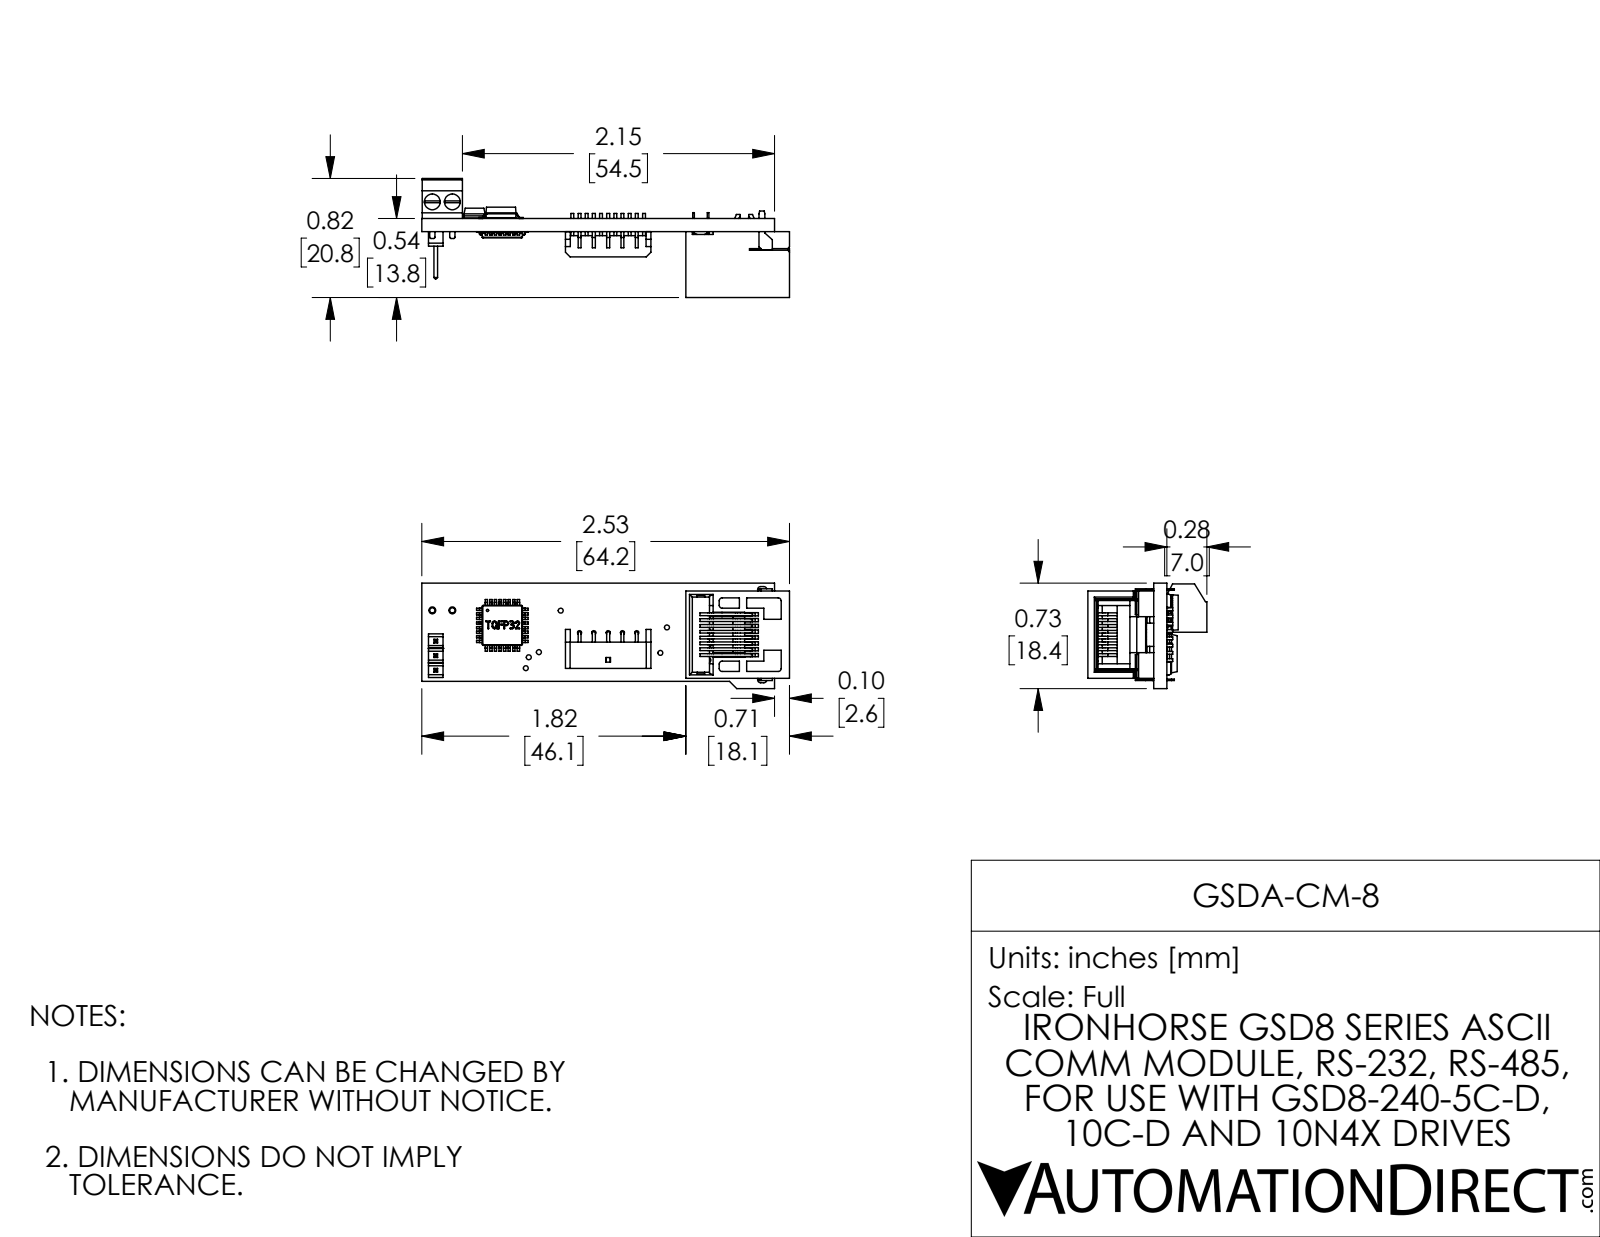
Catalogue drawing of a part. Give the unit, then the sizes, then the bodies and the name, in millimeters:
Units: millimetres
Overall size (bounding box): 64.2 × 20.8 × 18.4
Round holes (diameter × count): ⌀0.9 ×14, ⌀0.7 ×11, ⌀1 ×3, ⌀1.2 ×2, ⌀2 ×2, ⌀2.7 ×2, ⌀3.3 ×2, ⌀0.4 ×1, ⌀1.1 ×1, ⌀2.5 ×1
Round bosses / shafts (diameter × count): ⌀0.9 ×2
Partial cylindrical surfaces — rounded edges, fillets, slot ends (radius × count): R0.1 ×14, R0.5 ×9, R0.2 ×8, R0.3 ×6, R0.2 ×4, R0.5 ×4, R0.5 ×4, R0.8 ×3
Main face-to-face distances: 2.3, 15.2, 16.6, 1.4, 3, 0.5, 15.7, 17.1, 12.2, 13.8
Hole centre spacings: 2.4, 2.5, 4.2, 2.8, 5, 2.5, 6.6, 7.5
Volume: 4 440 mm³ · Surface area: 6 774 mm²
Bodies: 8 solids, 1705 faces (1259 planar, 356 cylindrical, 90 other)
Part name (STEP PRODUCT): GSDA-RTU-8
STEP written by: SolidWorks 2017 (AUTOMOTIVE_DESIGN)
